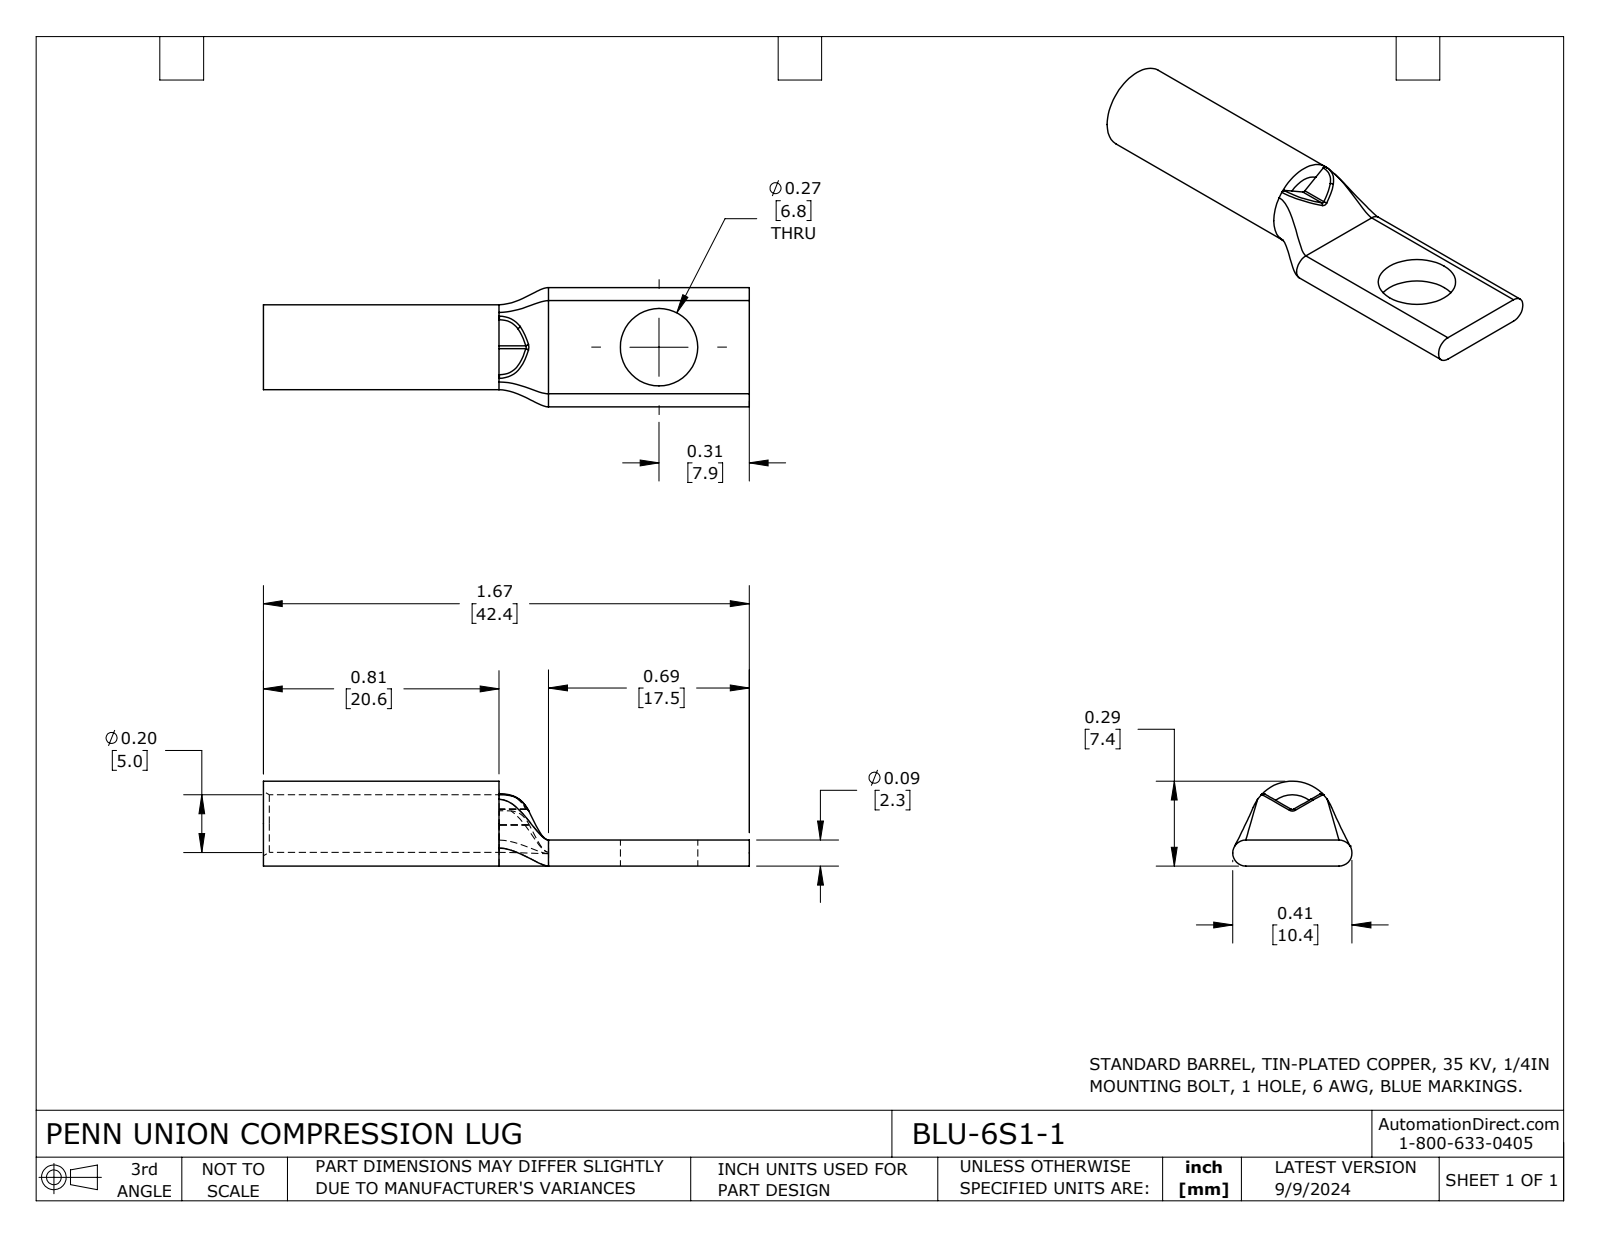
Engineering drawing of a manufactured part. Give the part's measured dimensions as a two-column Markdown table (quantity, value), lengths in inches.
| quantity | value |
| --- | --- |
| part name | BLU-6S1-1 |
| STEP written by | SolidWorks 2023 (CONFIG_CONTROL_DESIGN) |
| units | inches |
| bodies | 1 solid, 38 faces (11 planar, 11 cylindrical, 16 other) |
| overall size | 1.67 × 0.41 × 0.292 |
| volume | 0.054 in³ |
| surface area | 2.237 in² |
| round holes (diameter × count) | 0.198 × 1, 0.266 × 1 |
| round bosses / shafts (diameter × count) | 0.292 × 1 |
| partial cylindrical surfaces (radius × count) | 0.01 × 2, 0.045 × 2 |
| main face-to-face distances | 0.09, 1.67, 0.81, 0.86, 0.047, 0.98, 0.17, 0.69 |
